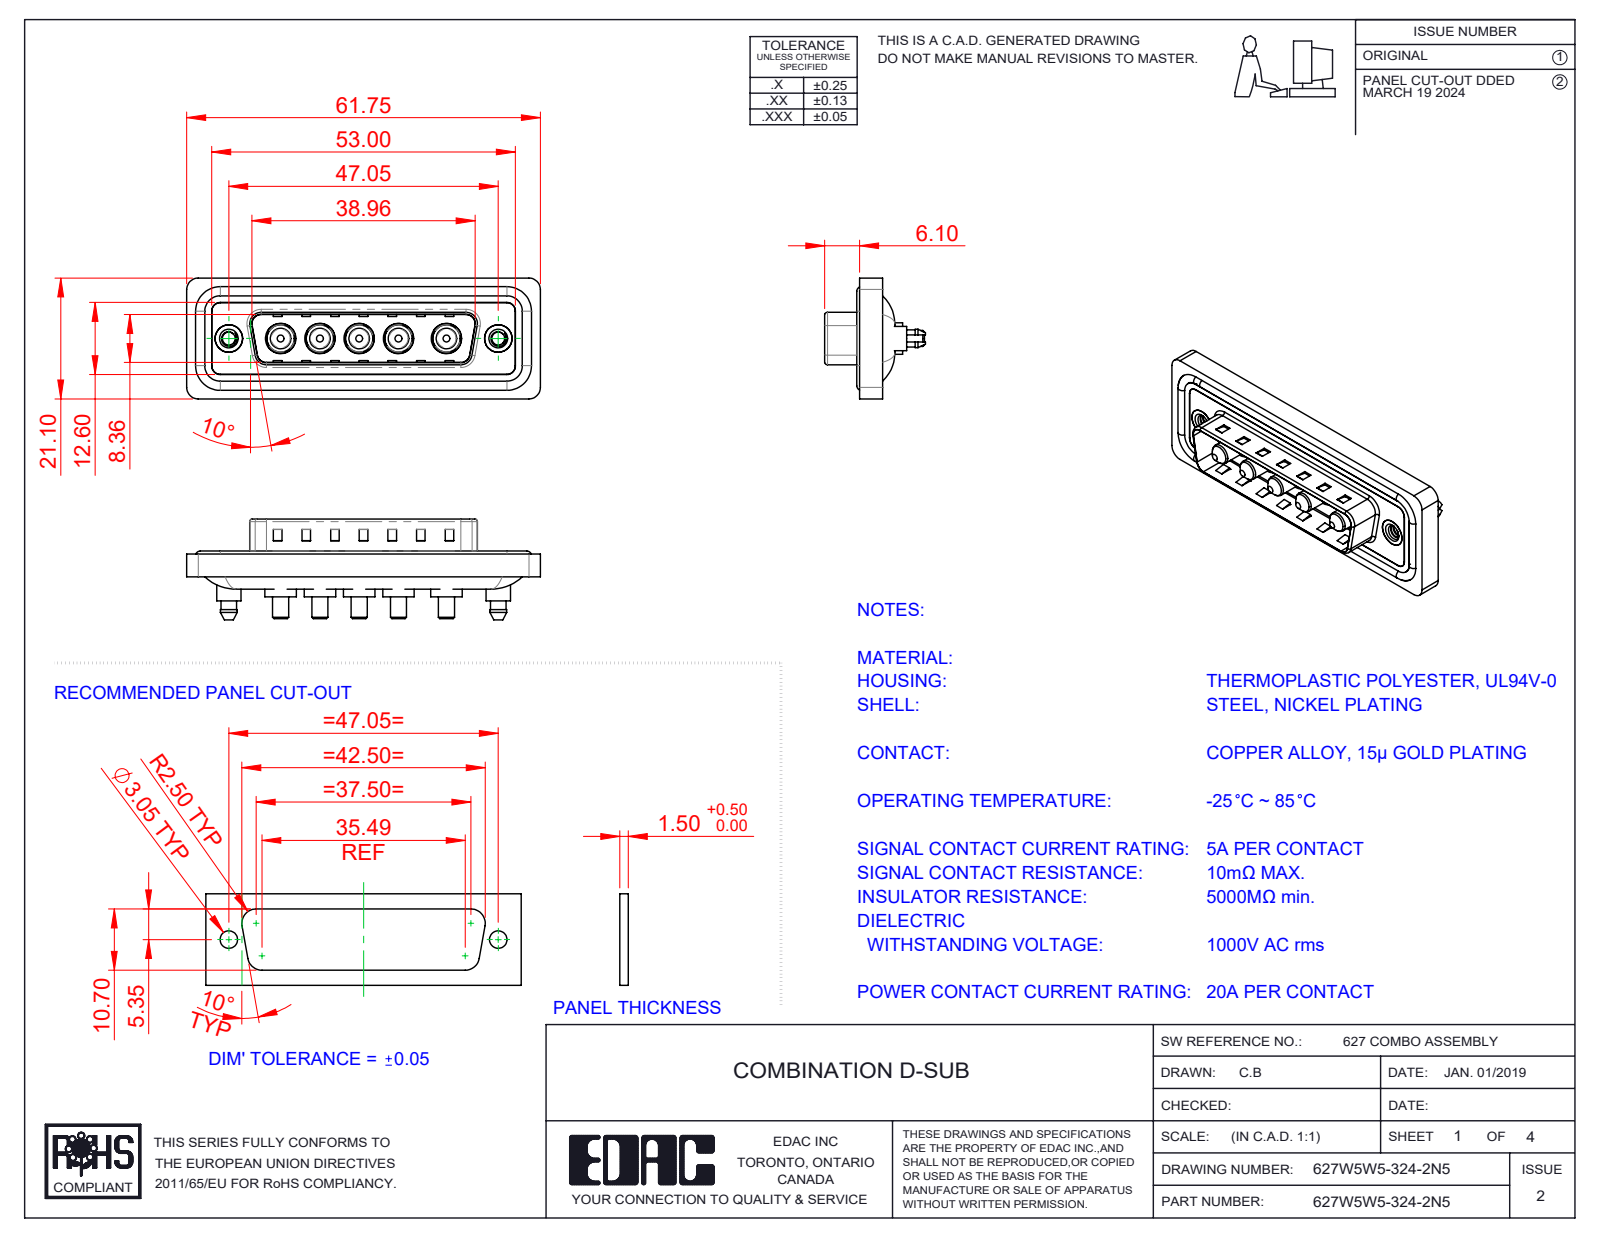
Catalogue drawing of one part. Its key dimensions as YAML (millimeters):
part_name: "627Combo Shell Rear_25 Contacts; Power Pin_20A S; 627Combo Housing_5W5; 627Combo Waterproof Housing_25 Contacts (+3 more)"
step_written_by: "SolidWorks 2023 (CONFIG_CONTROL_DESIGN)"
units: millimeters
bodies: {solids: 17, faces: 728, planar: 275, cylindrical: 315, other: 138}
overall_size: [61.75, 21.1, 17.6]
volume: 7606
surface_area: 12129
round_holes:
  - {diameter: 4.85, count: 5}
  - {diameter: 5.3, count: 5}
  - {diameter: 2.26, count: 2}
  - {diameter: 4, count: 2}
  - {diameter: 4.8, count: 2}
  - {diameter: 5, count: 2}
round_bosses_or_shafts:
  - {diameter: 5.5, count: 5}
  - {diameter: 5.2, count: 5}
  - {diameter: 4.75, count: 5}
  - {diameter: 3.75, count: 5}
  - {diameter: 3.6, count: 5}
  - {diameter: 2.8, count: 5}
  - {diameter: 1.6, count: 4}
  - {diameter: 5.4, count: 2}
partial_cylinders:
  - {radius: 1.5, count: 24}
  - {radius: 2, count: 18}
  - {radius: 1.6, count: 10}
  - {radius: 0.5, count: 8}
  - {radius: 2.1, count: 5}
  - {radius: 0.25, count: 4}
  - {radius: 0.6, count: 4}
  - {radius: 0.65, count: 4}
face_to_face_distances: [0.4, 1.5, 3.1, 1.1, 0.5, 1.6, 2.9, 0.82, 9.58, 5.65]
hole_center_spacings: [6.86, 9.04, 13.73, 38.01, 6.87, 8.37, 8.38, 9.05]
